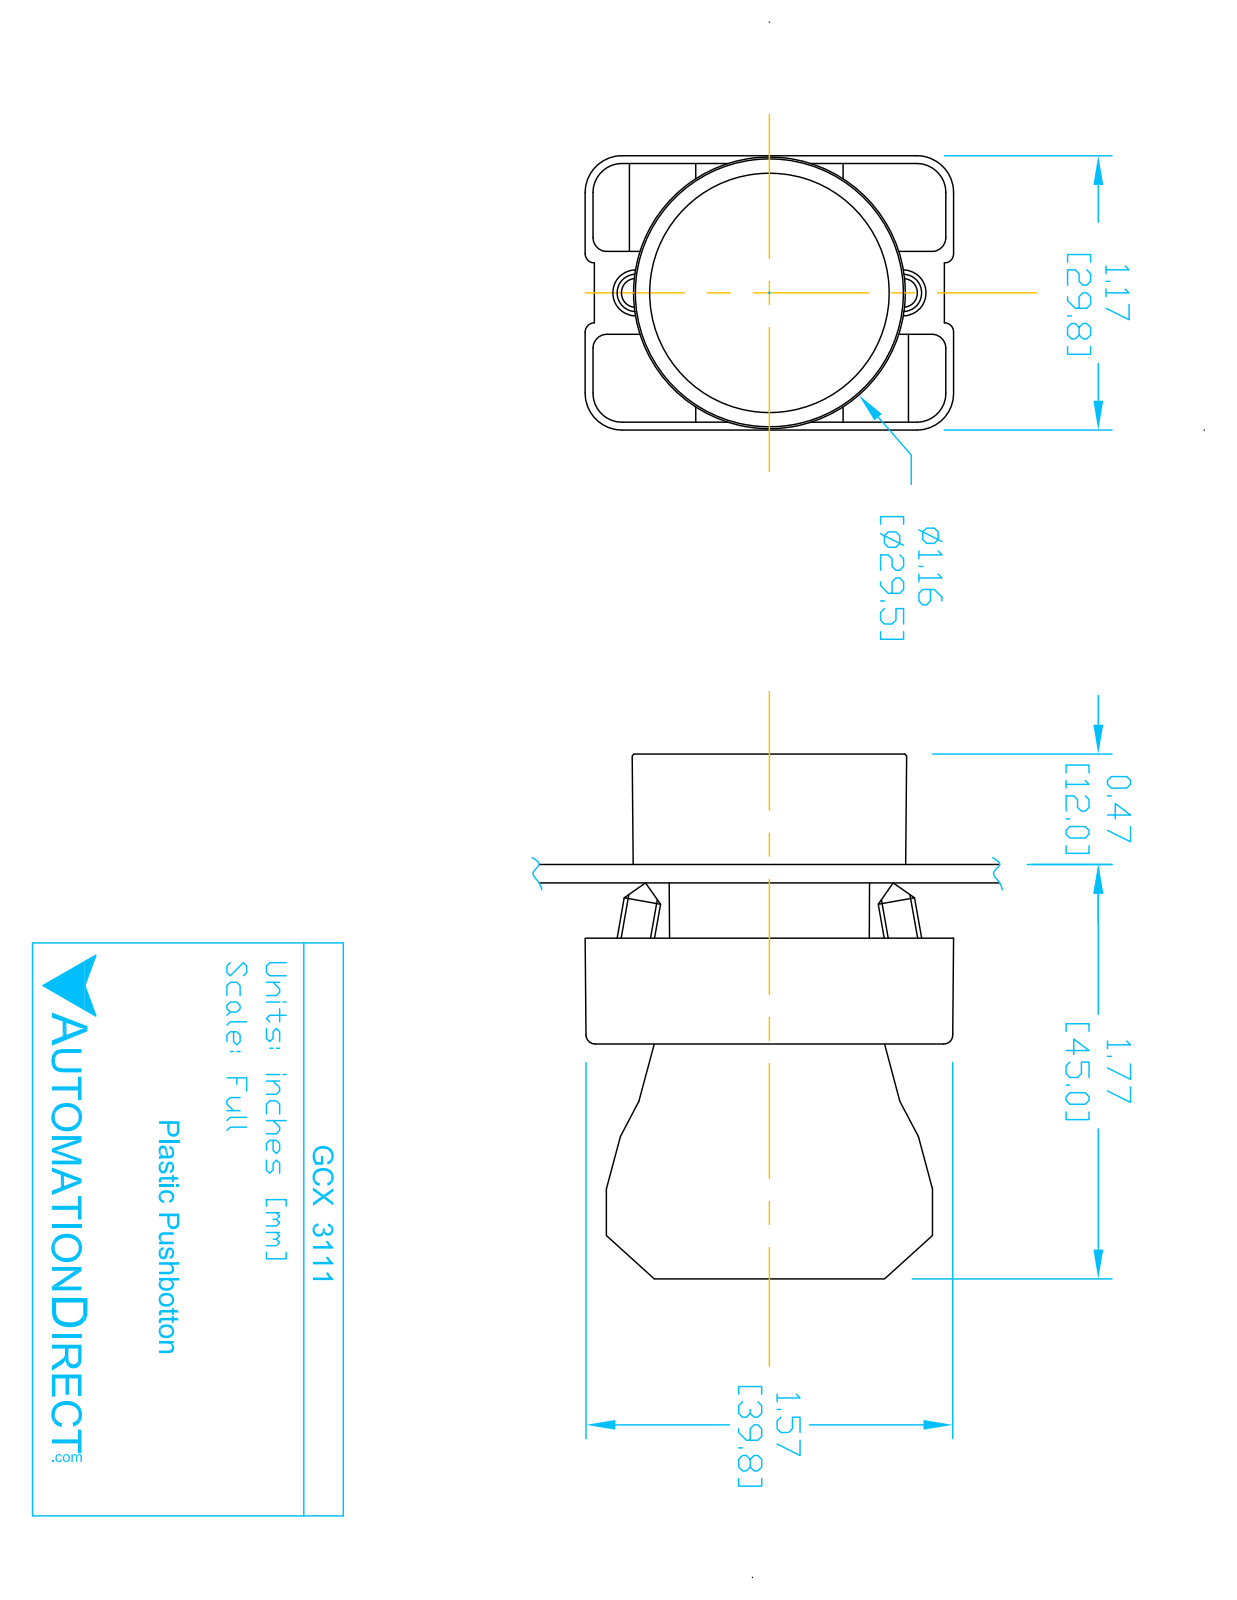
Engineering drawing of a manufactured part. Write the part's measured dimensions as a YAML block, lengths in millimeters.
part_name: "GCX3111 OPERATOR; ecx1030; ECX3029-2; GCX3111"
step_written_by: "SolidWorks 2016 (AUTOMOTIVE_DESIGN)"
units: millimeters
bodies: {solids: 6, faces: 383, planar: 222, cylindrical: 132, other: 29}
overall_size: [63.3, 40.2, 29.9]
volume: 25960
surface_area: 17080
round_holes:
  - {diameter: 2, count: 2}
  - {diameter: 3.1, count: 2}
  - {diameter: 3.3, count: 2}
  - {diameter: 2.2, count: 1}
  - {diameter: 5, count: 1}
  - {diameter: 22.3, count: 1}
  - {diameter: 22.6, count: 1}
  - {diameter: 26, count: 1}
round_bosses_or_shafts:
  - {diameter: 4, count: 2}
  - {diameter: 29.8, count: 1}
  - {diameter: 25.5, count: 1}
  - {diameter: 24, count: 1}
  - {diameter: 21.7, count: 1}
  - {diameter: 19.8, count: 1}
partial_cylinders:
  - {radius: 1.5, count: 24}
  - {radius: 1, count: 12}
  - {radius: 3.1, count: 12}
  - {radius: 4, count: 12}
  - {radius: 1, count: 4}
  - {radius: 3.3, count: 2}
  - {radius: 0.5, count: 1}
  - {radius: 1.6, count: 1}
face_to_face_distances: [14.7, 0.8, 30.3, 0.8, 12, 18.3, 7, 17.5, 15.2, 29.5]
hole_center_spacings: [6, 13.8, 12, 12.4]
